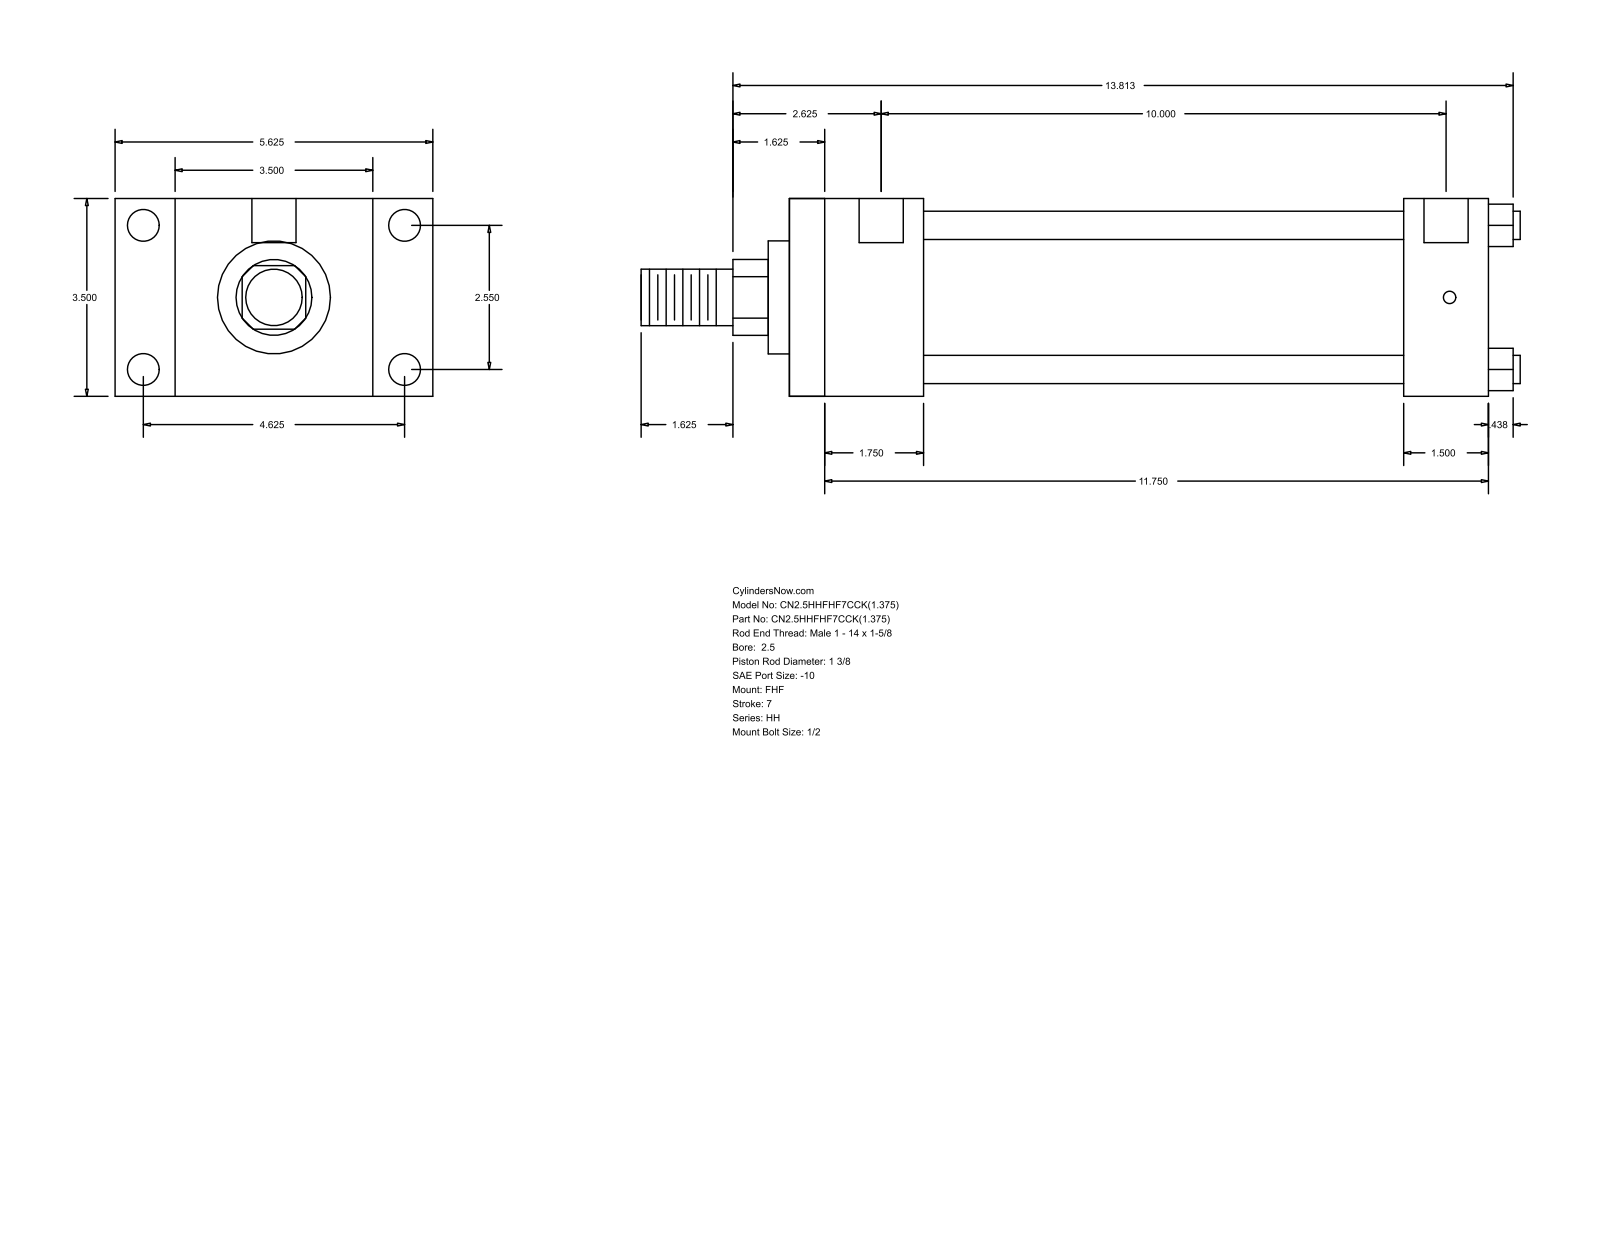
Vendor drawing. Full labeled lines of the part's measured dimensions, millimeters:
Part name (STEP PRODUCT): HH_FHF__0250_1.375
STEP written by: GSSL Pune (CONFIG_CONTROL_DESIGN)
Units: millimetres
Bodies: 0 solids, 88 faces (60 planar, 28 cylindrical, 0 other)
Overall size (bounding box): 395.29 × 142.88 × 88.9
Round holes (diameter × count): ⌀5.56 ×4, ⌀14.3 ×4, ⌀19.84 ×2
Round bosses / shafts (diameter × count): ⌀12.7 ×4, ⌀73.03 ×1, ⌀50.8 ×1, ⌀34.92 ×1, ⌀25.4 ×1
Partial cylindrical surfaces — rounded edges, fillets, slot ends (radius × count): R17.06 ×1
Main face-to-face distances: 88.9, 60.32, 26.99, 115.89, 314.33, 254.01, 142.88, 276.22, 215.9, 38.11
Hole centre spacings: 1.58, 64.76, 117.48, 134.15, 255.59, 257.17, 254.01
